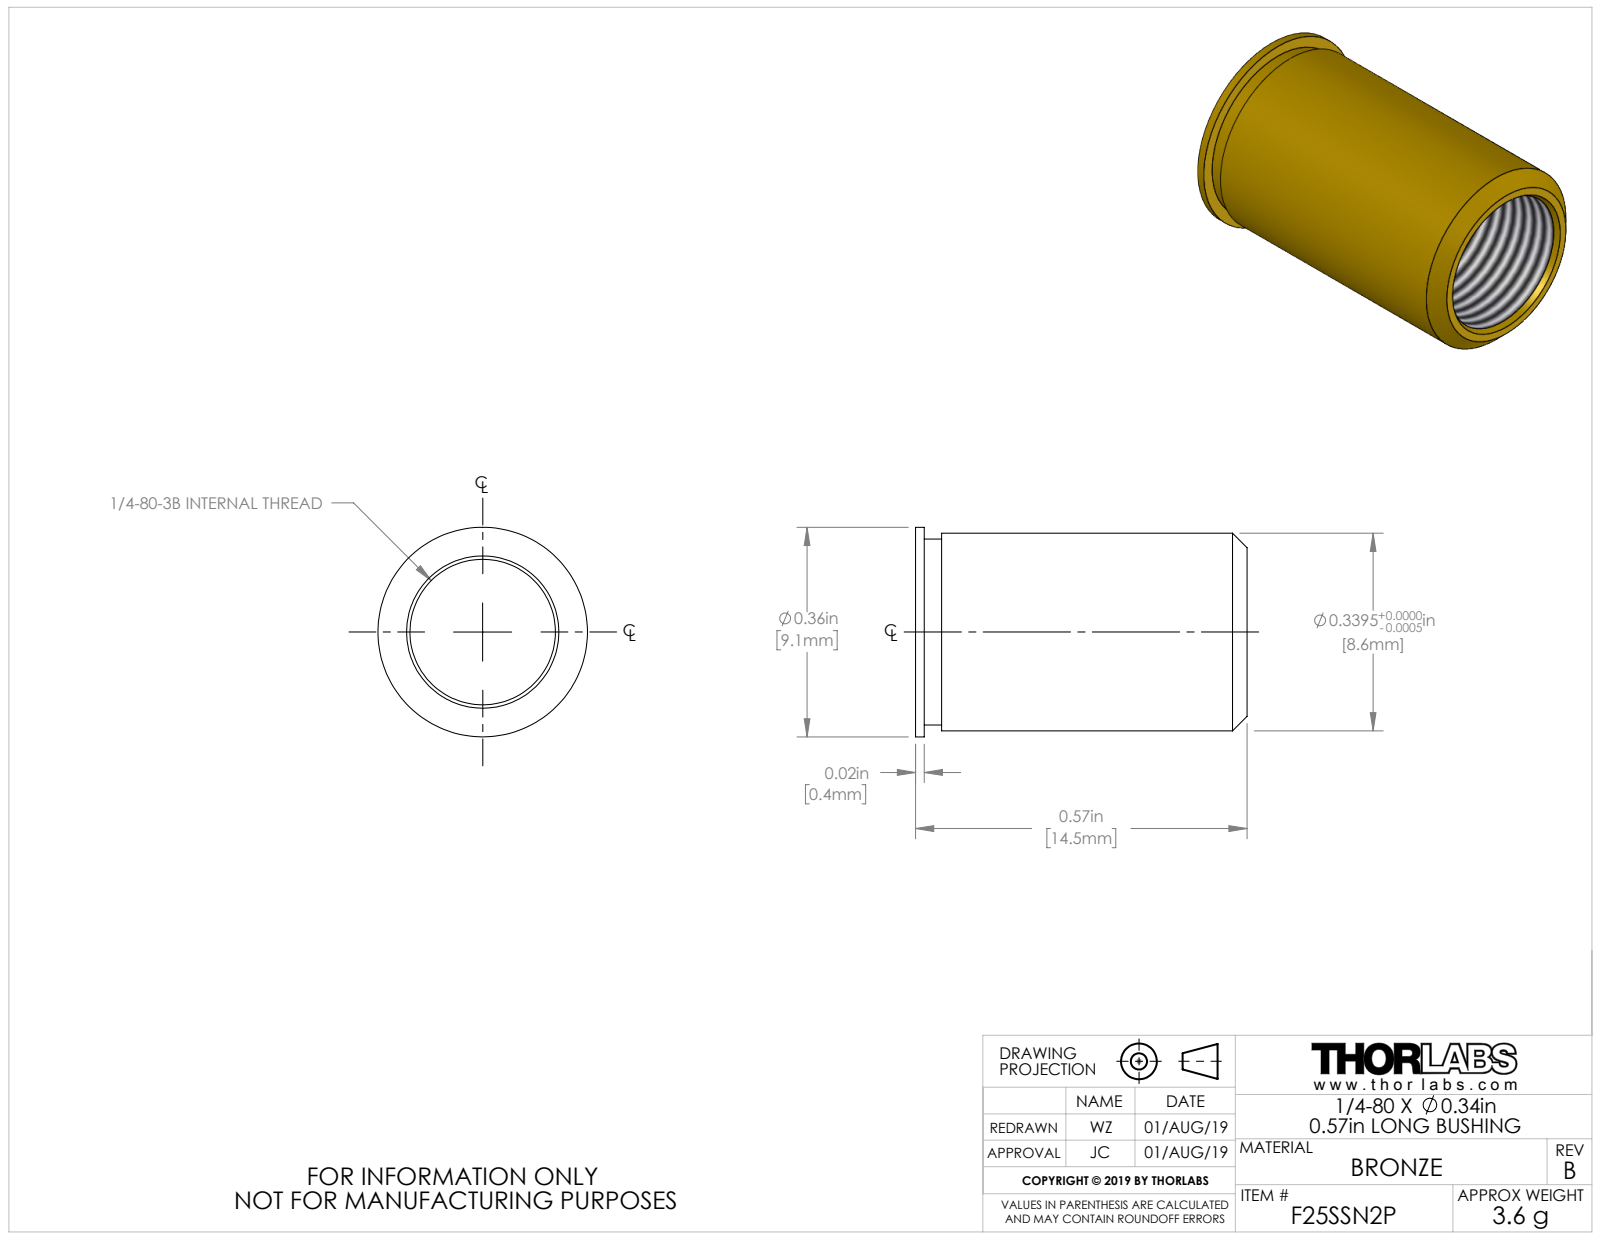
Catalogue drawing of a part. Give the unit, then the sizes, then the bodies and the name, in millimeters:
Units: millimetres
Overall size (bounding box): 14.48 × 9.14 × 9.14
Round holes (diameter × count): ⌀6.35 ×1
Round bosses / shafts (diameter × count): ⌀9.14 ×1, ⌀8.62 ×1, ⌀8.12 ×1
Main face-to-face distances: 0.38, 14.48, 14.1, 1.14, 0.76, 13.34
Volume: 379 mm³ · Surface area: 747 mm²
Bodies: 1 solid, 18 faces (4 planar, 8 cylindrical, 6 other)
Part name (STEP PRODUCT): 18992-E0W
STEP written by: SolidWorks 2007 (AUTOMOTIVE_DESIGN)
